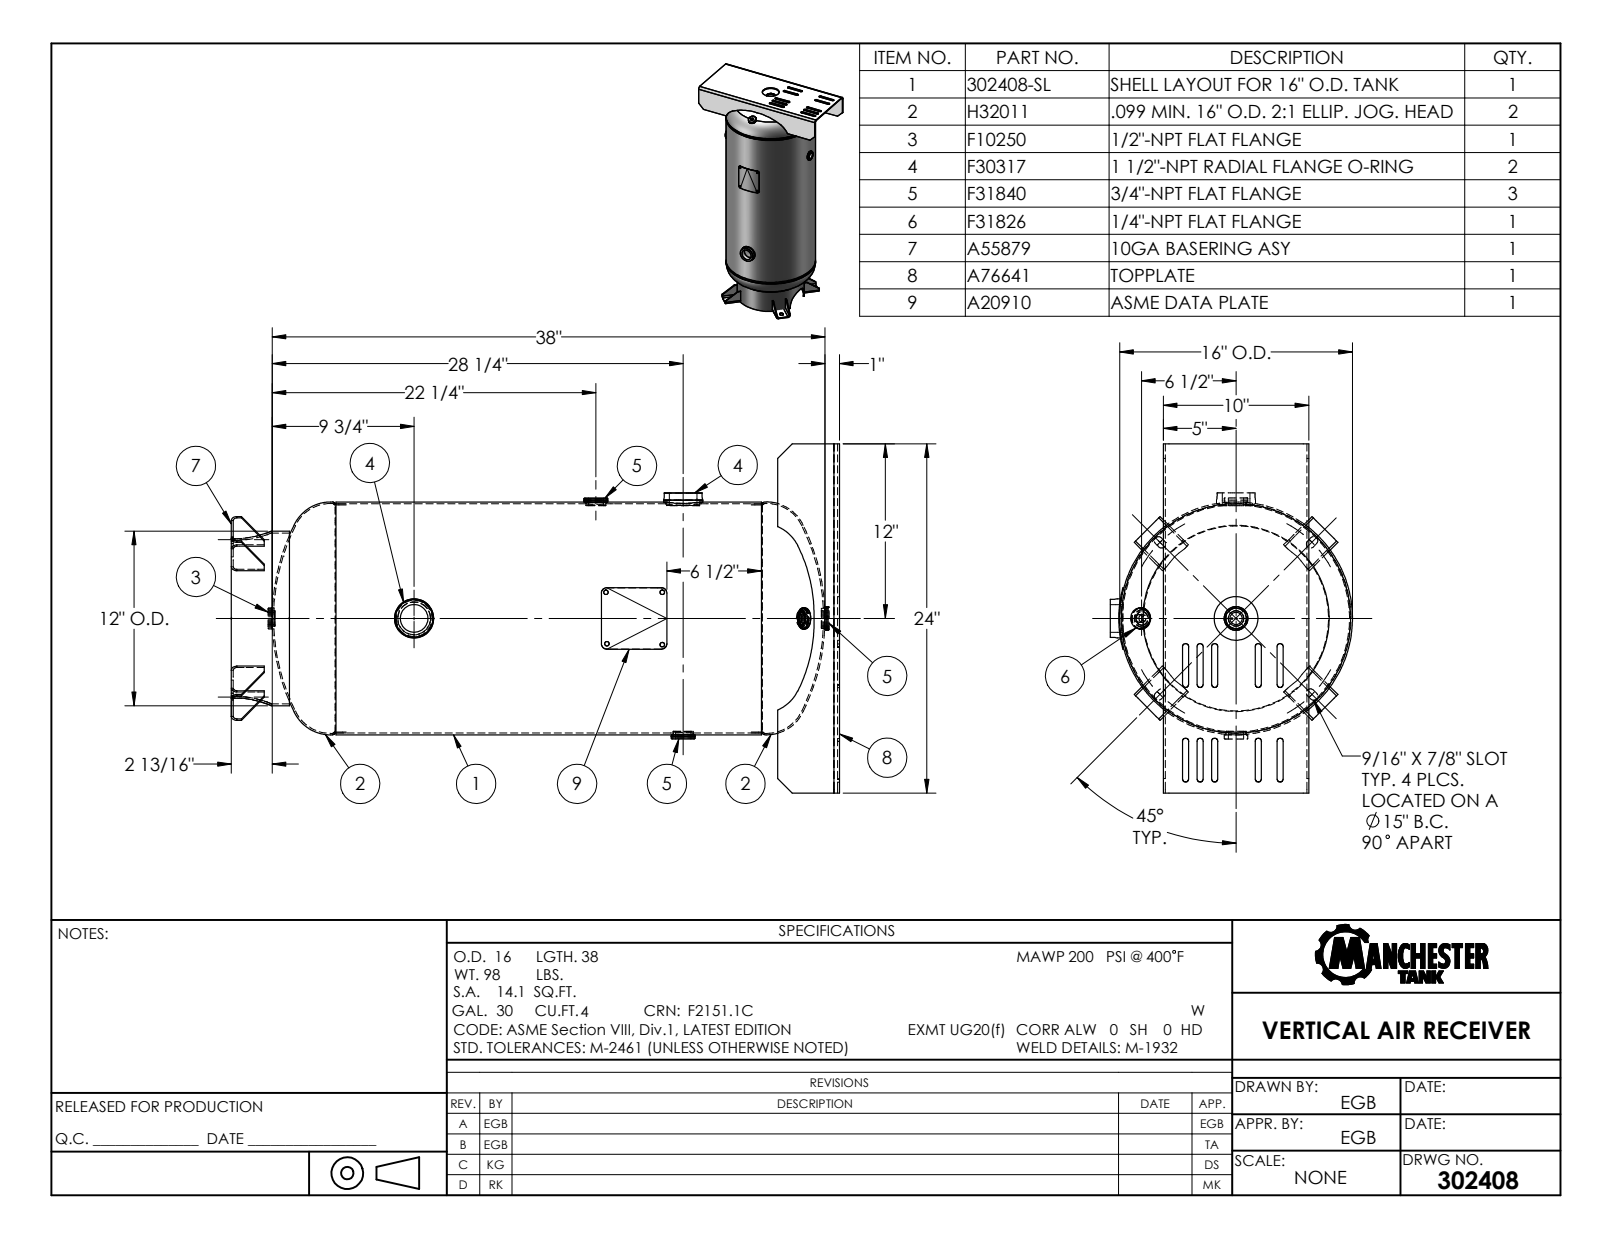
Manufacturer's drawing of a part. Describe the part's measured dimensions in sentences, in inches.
The part is named "302408". Its 3-D file was written by "SolidWorks 2011 (CONFIG_CONTROL_DESIGN)". It is 0 solids with 317 faces: 139 planar, 107 cylindrical and 71 other. Overall it measures 41.751 by 24 by 16.645 inches. Round holes: 3 of diameter 1.05, 2 of diameter 1.9, 1 of diameter 0.54, 1 of diameter 0.84, 1 of diameter 3, 1 of diameter 11.731, 1 of diameter 15.748. Round bosses or shafts: 2 of diameter 2.688, 2 of diameter 1.63, 2 of diameter 1.45, 2 of diameter 1.438, 1 of diameter 16, 1 of diameter 15.74, 1 of diameter 12, 1 of diameter 1.625. Partial cylindrical surfaces (rounded edges, fillets, slot ends): 20 of radius 0.203, 8 of radius 0.25, 8 of radius 0.281, 8 of radius 0.384, 2 of radius 0.075, 2 of radius 0.209, 2 of radius 2.826, 2 of radius 10.471. The main face-to-face distances are 0.134, 9.866, 9.732, 10, 41.617, 2.383, 41.751, 41.483, 2.517, 2.25. The hole center spacings are 6.
